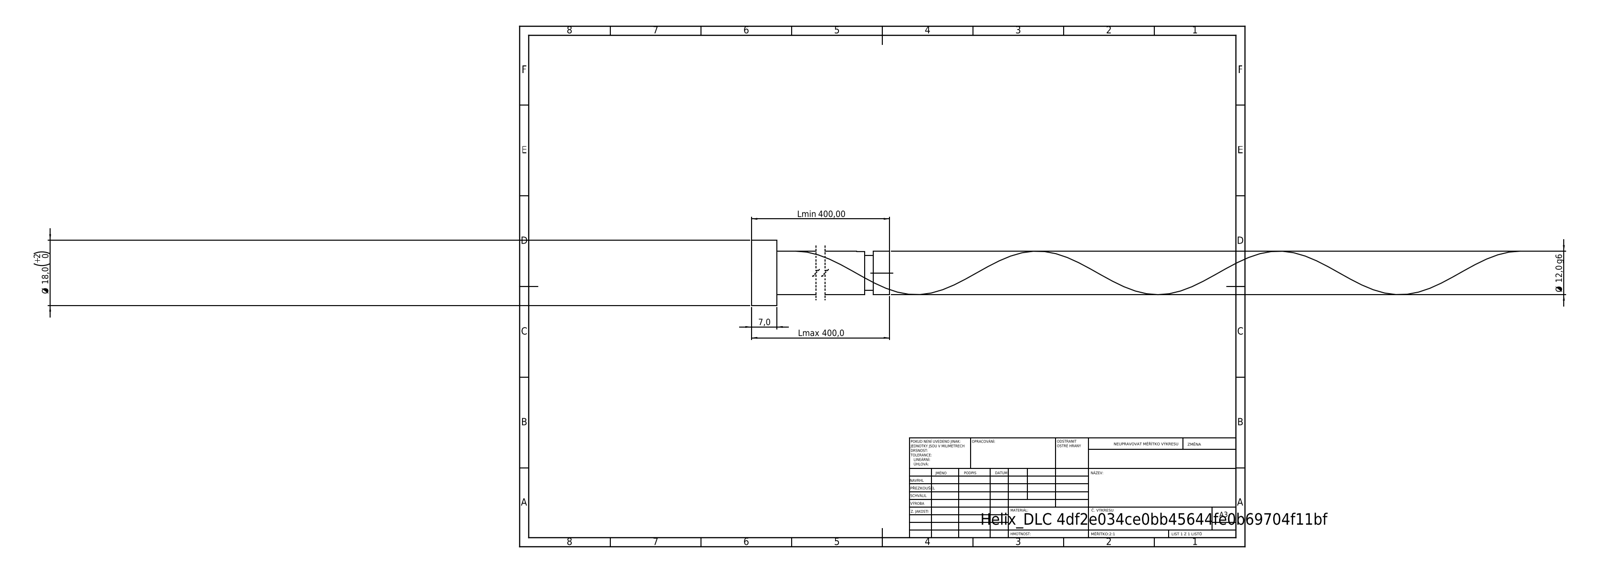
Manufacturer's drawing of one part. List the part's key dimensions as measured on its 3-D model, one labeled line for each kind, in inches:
STEP written by: SolidWorks 2019 (CONFIG_CONTROL_DESIGN)
Units: inches
Bodies: 1 solid, 21 faces (6 planar, 14 cylindrical, 1 other)
Overall size (bounding box): 15.748 × 0.709 × 0.709
Volume: 2.789 in³ · Surface area: 24.89 in²
Round bosses / shafts (diameter × count): ⌀0.709 ×1, ⌀0.472 ×1, ⌀0.378 ×1
Main face-to-face distances: 0.276, 15.748, 15.472, 15.569, 15.293, 0.179, 15.474, 15.199, 0.094, 0.274
